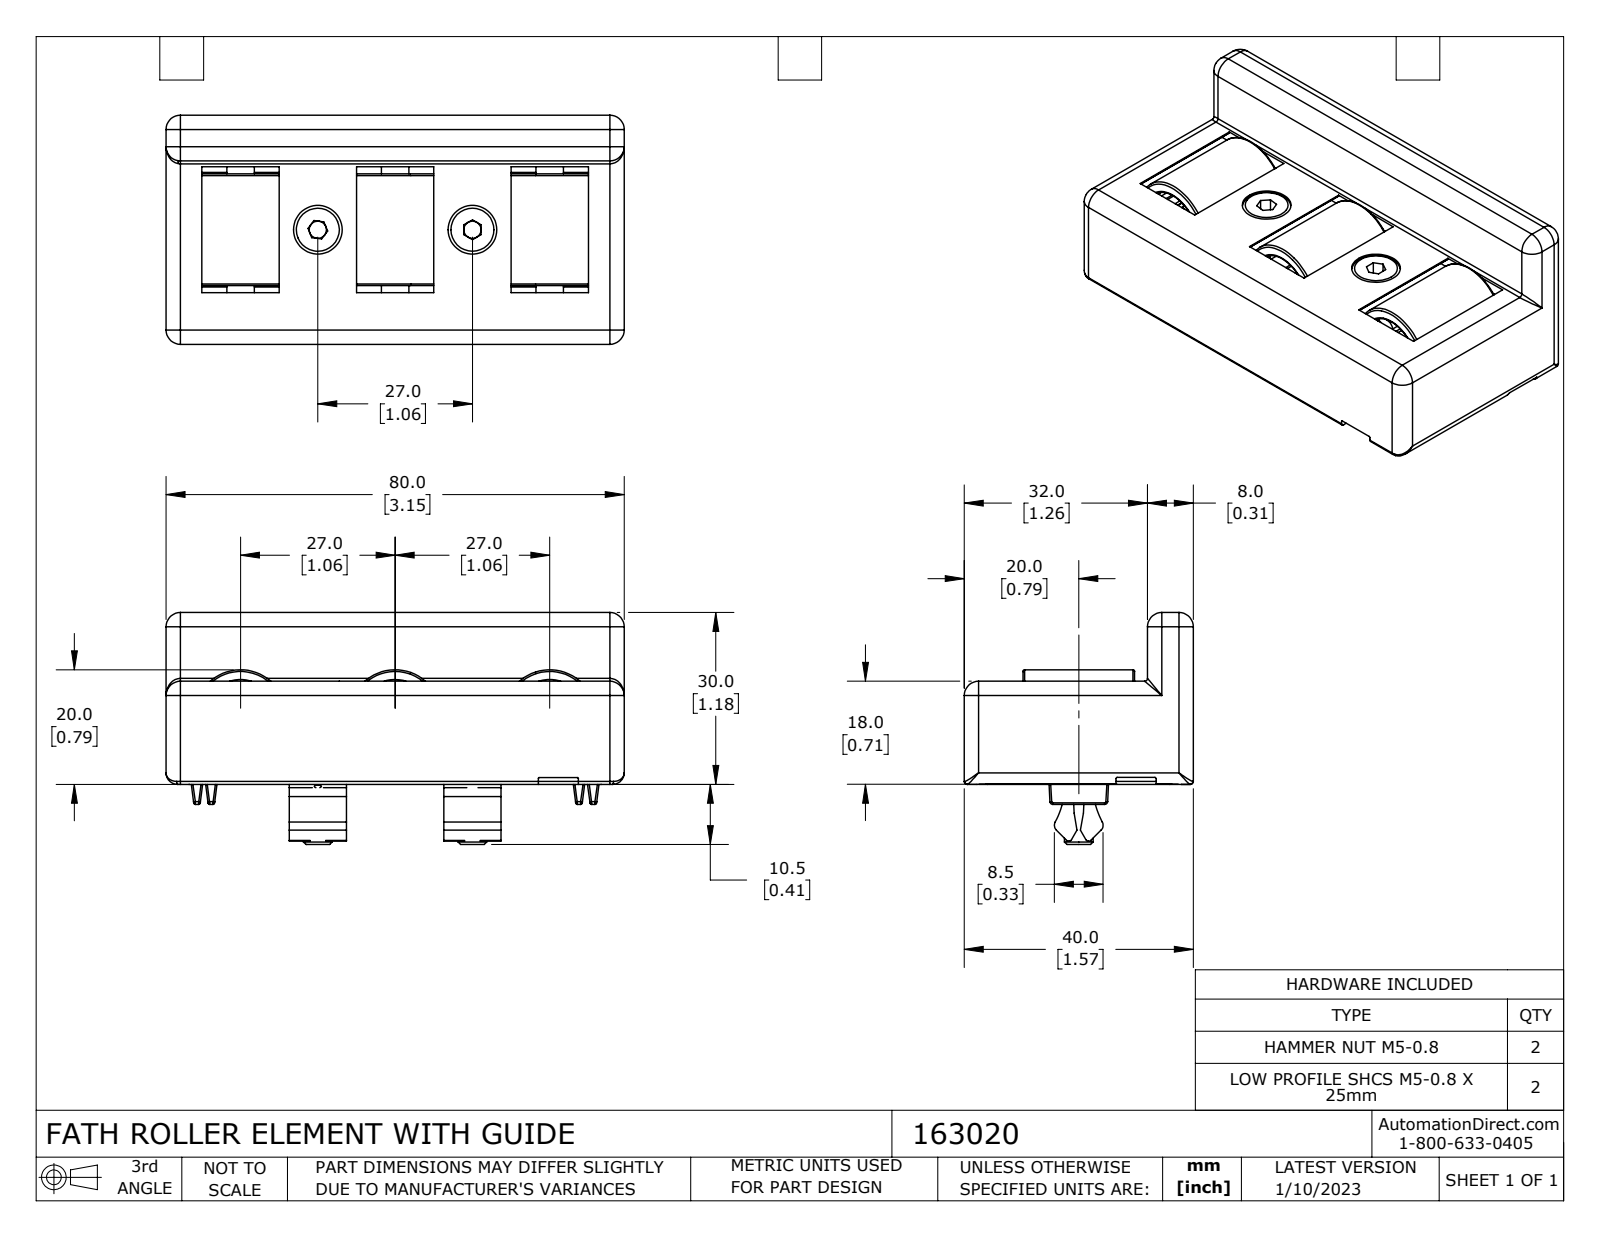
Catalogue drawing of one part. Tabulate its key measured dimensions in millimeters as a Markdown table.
| quantity | value |
| --- | --- |
| part name | 163020 |
| STEP written by | SolidWorks 2021 (CONFIG_CONTROL_DESIGN) |
| units | millimeters |
| bodies | 9 solids, 1143 faces (580 planar, 399 cylindrical, 164 other) |
| overall size | 80 × 40.5 × 40 |
| volume | 43 527 mm³ |
| surface area | 41 994 mm² |
| round holes (diameter × count) | 12 × 3, 4.2 × 2, 4.4 × 2, 5 × 2, 5.2 × 2, 8.5 × 2 |
| round bosses / shafts (diameter × count) | 16 × 3, 4.8 × 3 |
| partial cylindrical surfaces (radius × count) | 0.5 × 83, 1 × 28, 0.3 × 24, 2.5 × 19, 0.2 × 12, 2 × 10, 0.1 × 9, 1.35 × 9 |
| main face-to-face distances | 2, 16, 2.1, 3, 14, 38, 5, 3.9, 1.9, 1.8 |
| hole center spacings | 27, 8.5, 35.5, 44, 54 |
